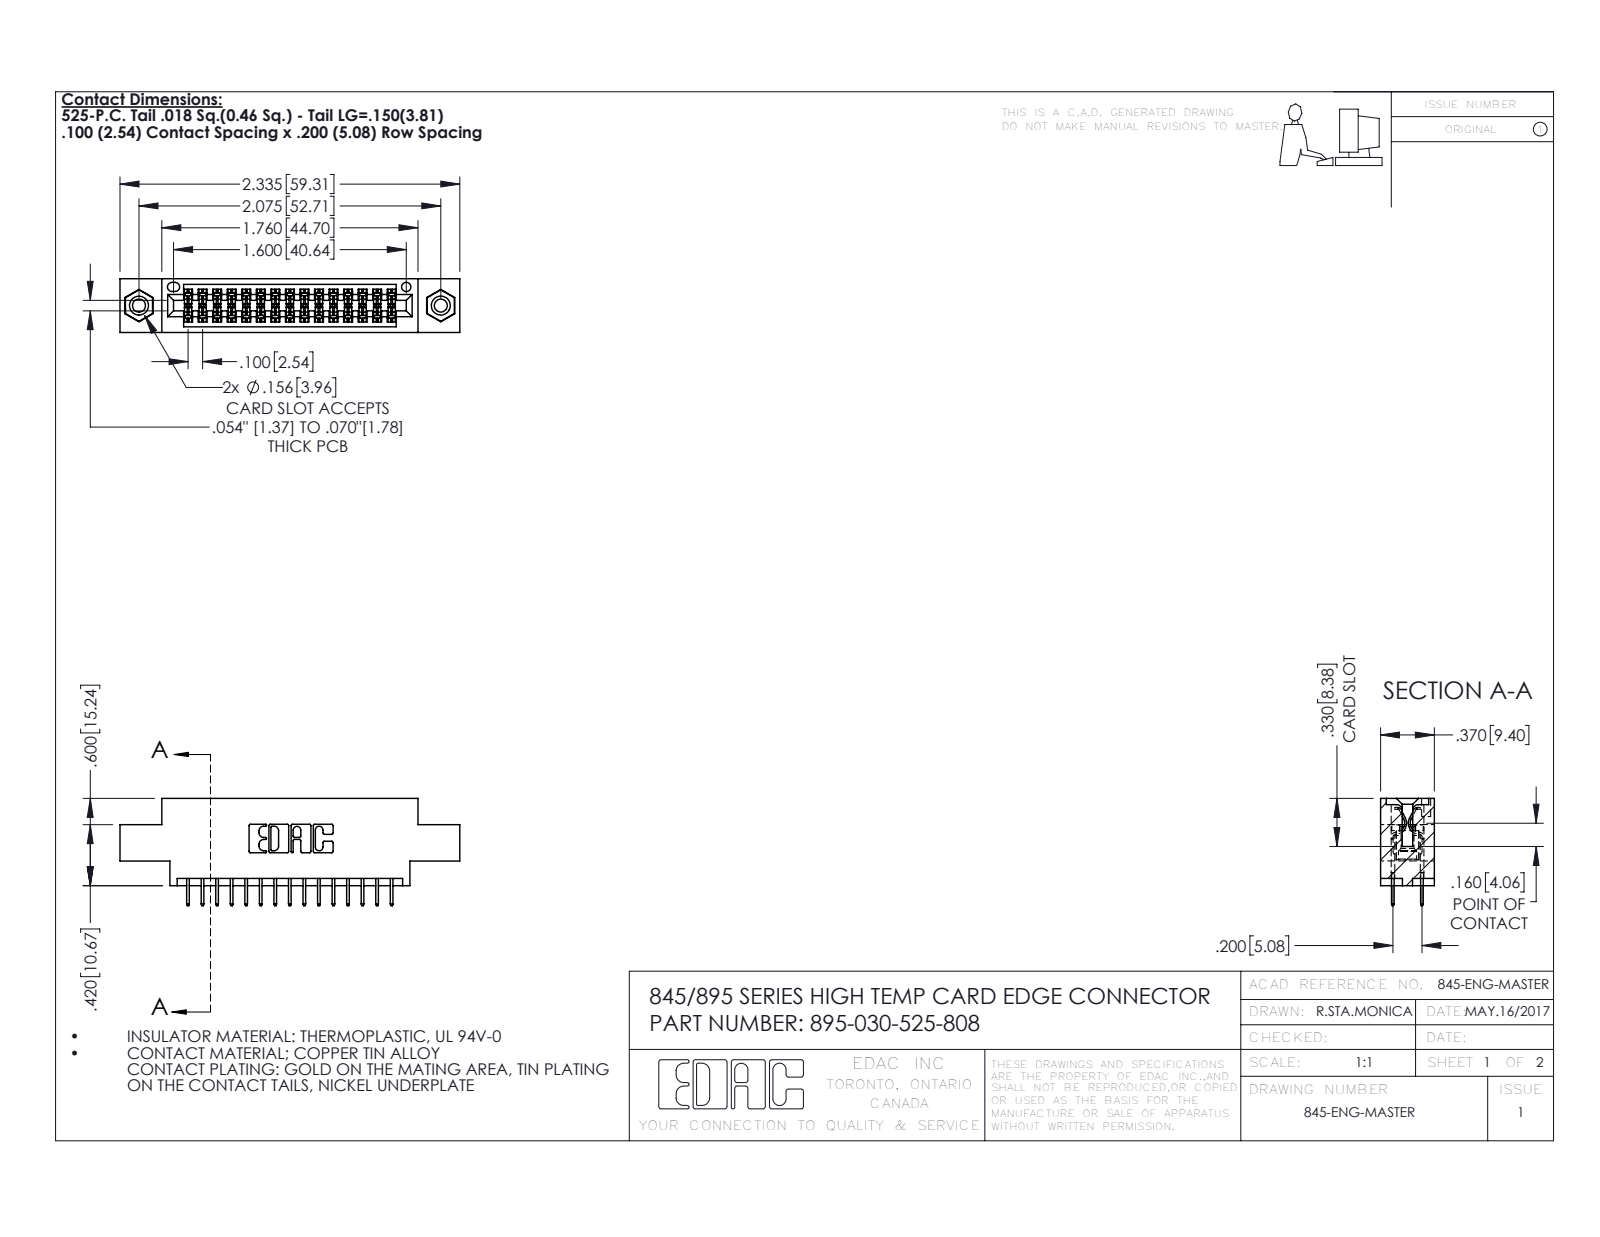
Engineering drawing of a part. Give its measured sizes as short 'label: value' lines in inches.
name: 845 Part_0.170 Offset - 0.156 Dia-TI; 895-030-525-808; 345-292-001_345-293-125; 345-250-001_345-250-003-102
written by: SolidWorks 2020 (CONFIG_CONTROL_DESIGN)
unit: in
bodies: 33 solids, 1810 faces (1286 planar, 508 cylindrical, 16 other)
size: 2.335 × 0.737 × 0.37
volume: 0.326 in³; area: 11.44 in²
holes: 2× ⌀0.089, 2× ⌀0.125, 2× ⌀0.156, 1× ⌀0.064
bosses: 2× ⌀0.155
rounds: 45× R0.006, 22× R0.01, 6× R0.007, 6× R0.031, 3× R0.026, 2× R0.014, 2× R0.019, 2× R0.022
face distances: 0.072, 0.298, 0.37, 0.2, 0.098, 0.272, 0.025, 0.225, 0.1, 0.175
hole spacings: 0.27, 1.842, 2.075
